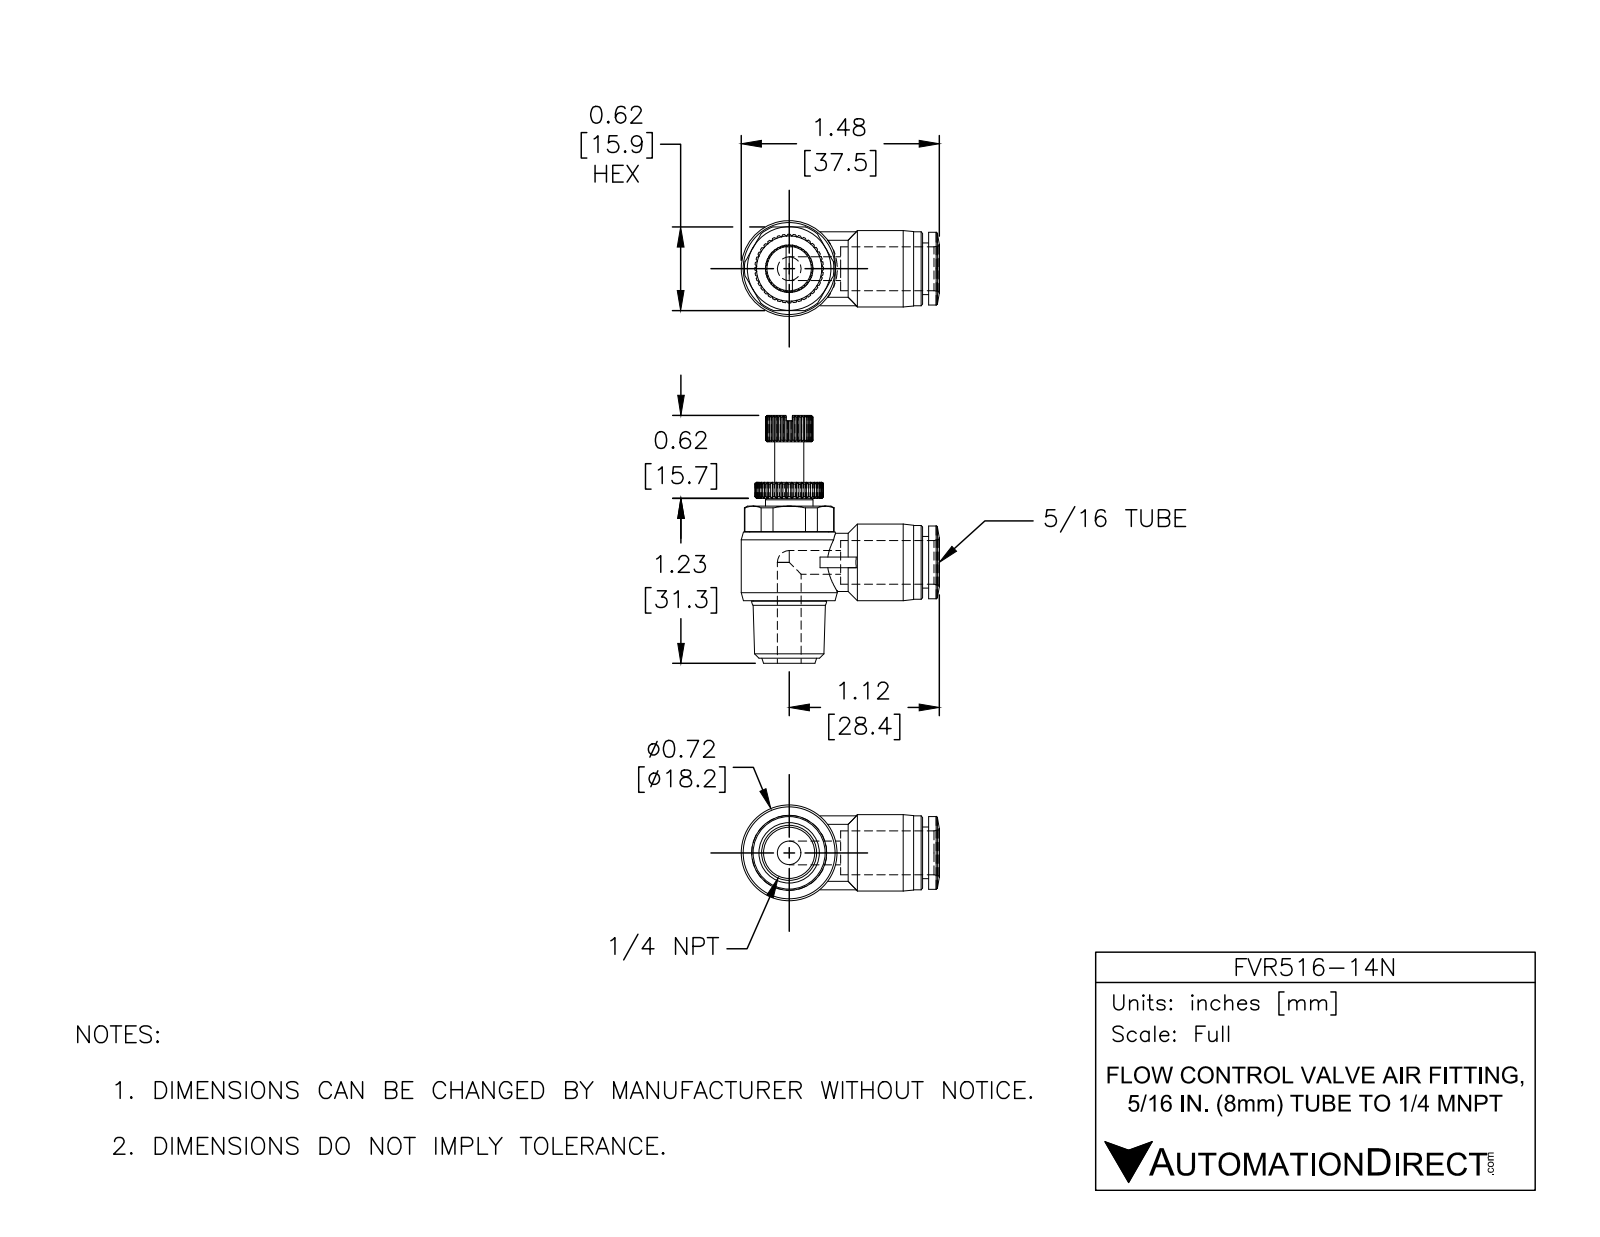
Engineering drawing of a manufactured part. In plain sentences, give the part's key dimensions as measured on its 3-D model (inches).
The part is named "FVR516-14N". Its 3-D file was written by "SolidWorks 2015 (CONFIG_CONTROL_DESIGN)". It is 1 solid with 423 faces: 187 planar, 112 cylindrical and 124 other. Overall it measures 1.85 by 1.478 by 0.717 inches. Its volume is 0.51 cubic inches and its surface area 7.237 square inches. Round holes: 2 of diameter 0.177, 1 of diameter 0.327. Round bosses or shafts: 1 of diameter 0.717, 1 of diameter 0.591, 1 of diameter 0.571, 1 of diameter 0.551, 1 of diameter 0.543, 1 of diameter 0.539, 1 of diameter 0.433, 1 of diameter 0.386. Partial cylindrical surfaces (rounded edges, fillets, slot ends): 1 of radius 0.256, 1 of radius 0.335. The main face-to-face distances are 0.177, 0.705, 0.882, 0.624, 0.045, 0.764, 0.059, 0.118, 0.512, 0.193.
